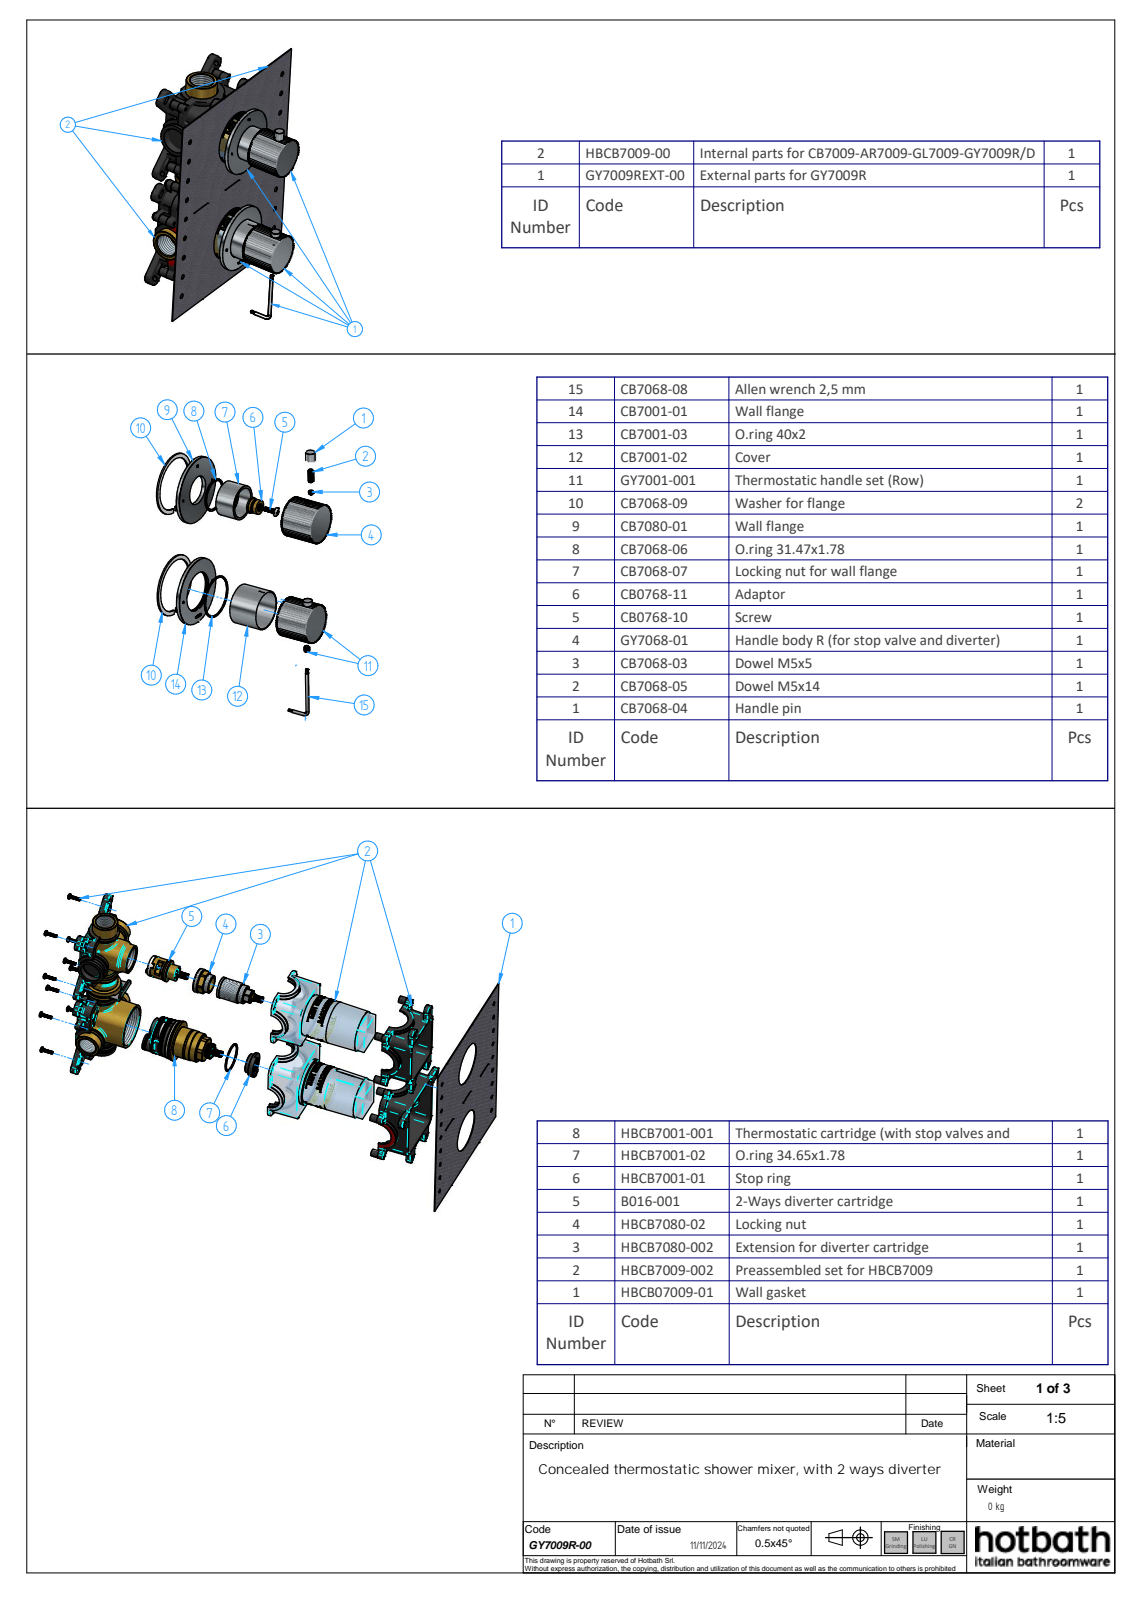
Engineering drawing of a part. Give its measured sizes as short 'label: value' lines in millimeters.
name: GY7009R-00; GY7009REXT-00_oa_0; CB7001-02; CB7001-01 (+8 more)
written by: Solid Edge (AUTOMOTIVE_DESIGN)
unit: mm
bodies: 19 solids, 2200 faces (569 planar, 666 cylindrical, 965 other)
size: 192 × 72 × 68.3
volume: 72 021 mm³; area: 67 105 mm²
holes: 2× ⌀4.13, 2× ⌀5.2, 2× ⌀38, 2× ⌀57, 2× ⌀67, 1× ⌀2, 1× ⌀2.46, 1× ⌀3.2, 1× ⌀4, 1× ⌀4.5, 1× ⌀7, 1× ⌀10.2
bosses: 2× ⌀72, 2× ⌀66, 2× ⌀10, 2× ⌀5, 2× ⌀4, 1× ⌀42, 1× ⌀17, 1× ⌀15.15
rounds: 354× R0.1, 8× R4.5, 2× R0.2, 2× R0.56, 2× R0.73, 2× R1, 2× R2.1, 2× R9.5
face distances: 4, 3, 1, 1.5, 4.5, 0.5, 55.43, 55.53, 54.93, 55.03
hole spacings: 2, 2.06, 2.1, 12.5, 14.9, 92.6, 105.1, 107.5
